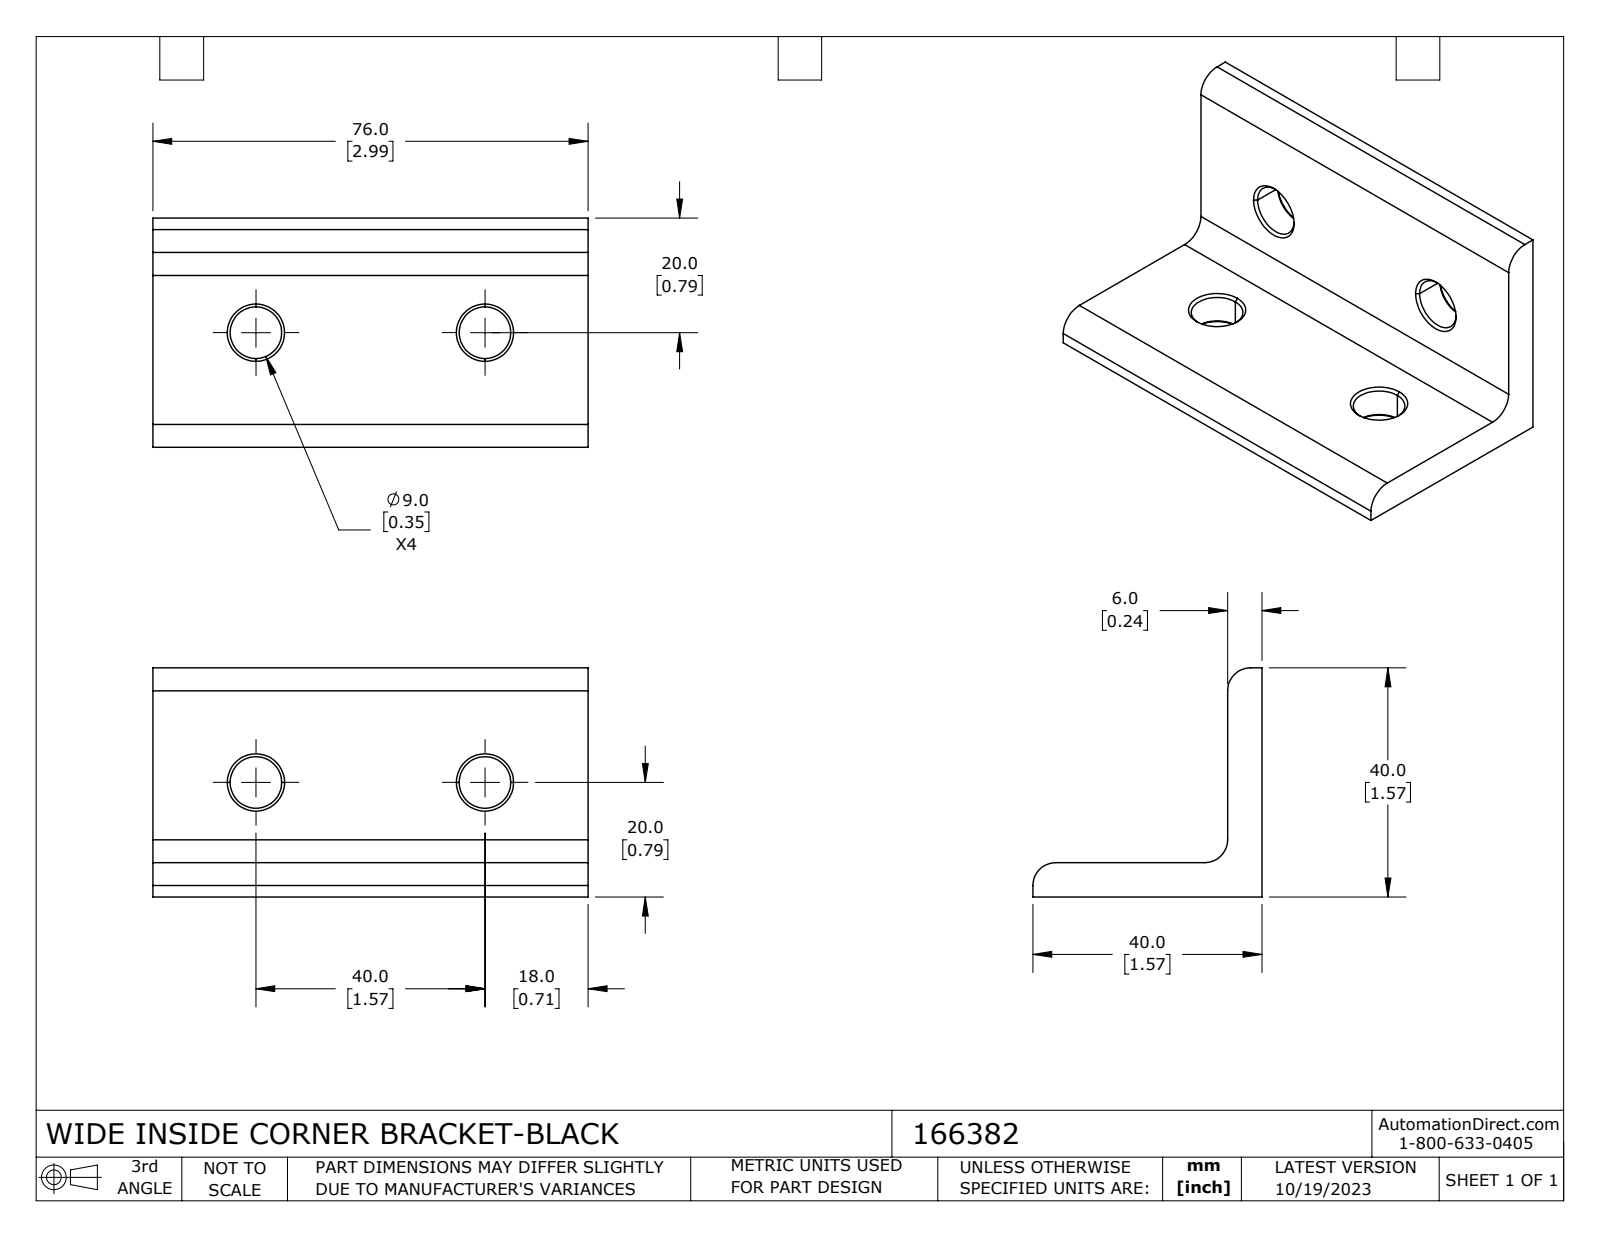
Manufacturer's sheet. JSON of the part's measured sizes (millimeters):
{"part_name": "166382", "step_written_by": "SolidWorks 2023 (CONFIG_CONTROL_DESIGN)", "units": "millimeters", "bodies": {"solids": 1, "faces": 35, "planar": 8, "cylindrical": 11, "other": 16}, "overall_size": [76, 40, 40], "volume_mm3": 31927, "surface_area_mm2": 12756, "round_holes": [[9, 4]], "partial_cylinders_radius": [[4, 3]], "face_to_face_distances": [6, 76, 40, 34], "hole_center_spacings": [40]}
